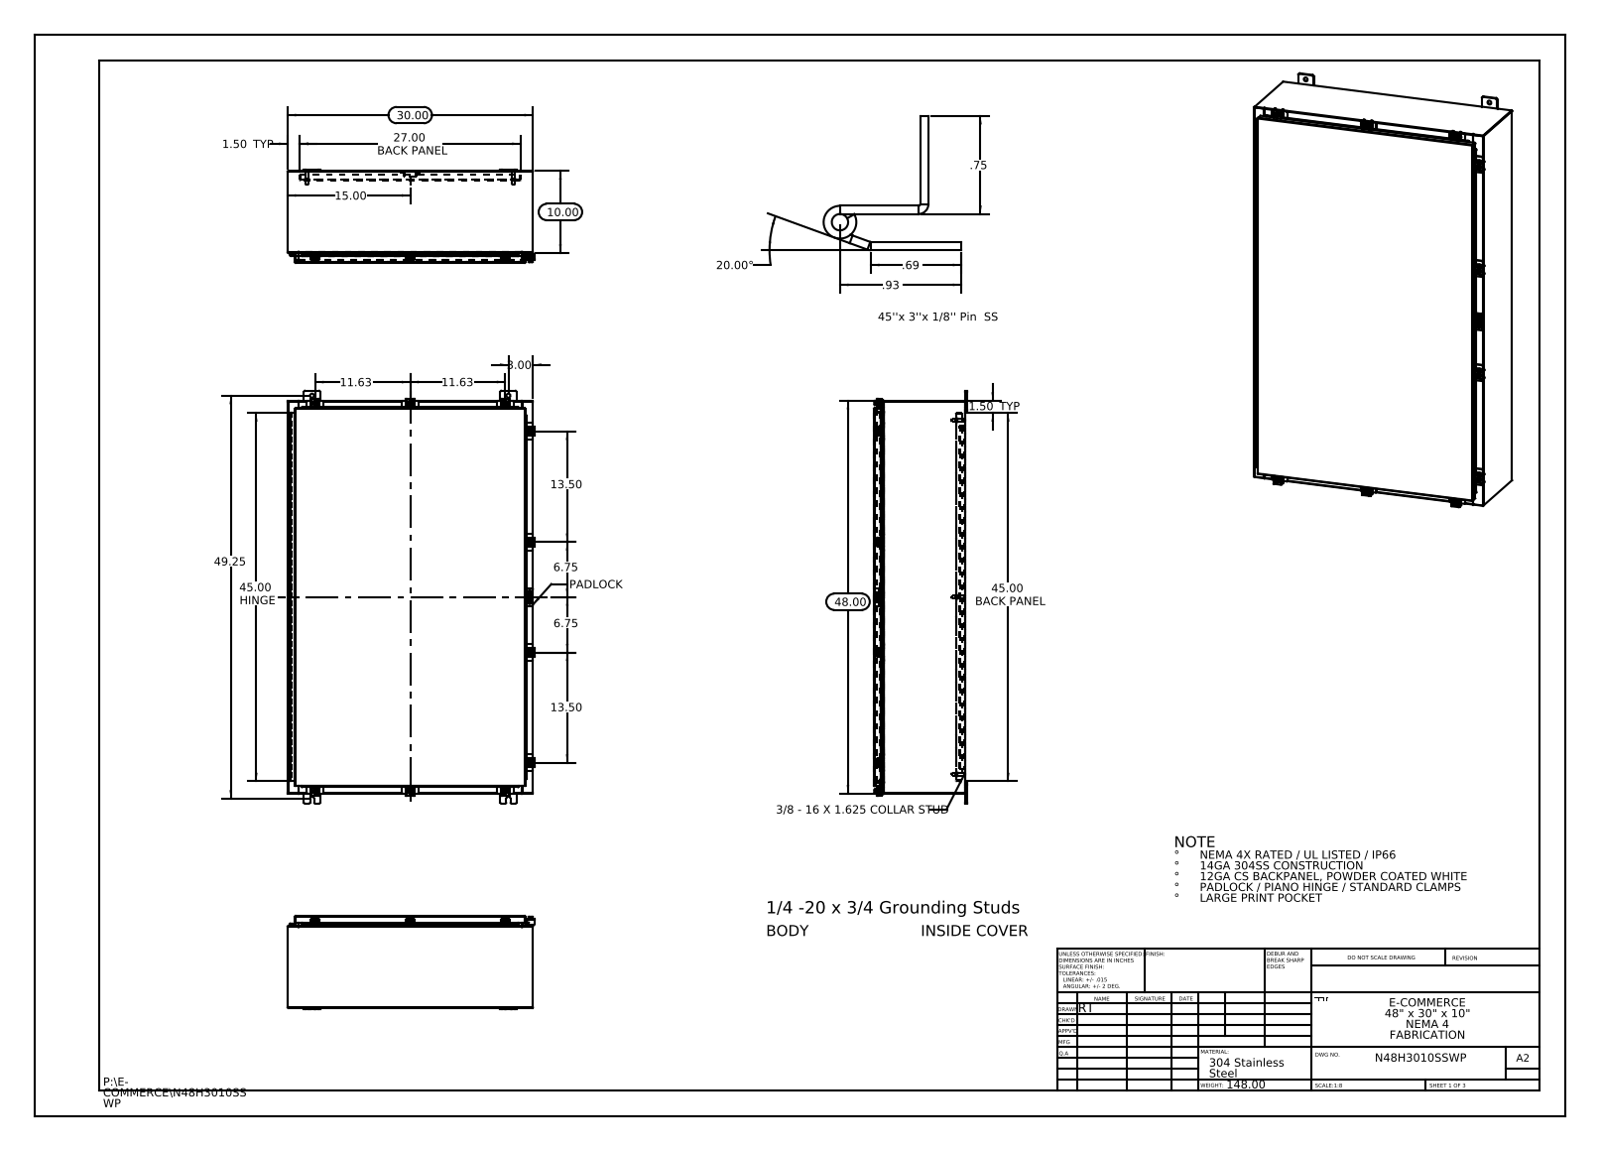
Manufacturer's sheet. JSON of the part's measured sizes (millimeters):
{"part_name": "N48H3010SSWP Cover; N48H3010SSWP Enclosure Stiffener; N48H3010SSWP Padlock Staple; N48H3010SSWP Top (+8 more)", "step_written_by": "SolidWorks 2013 (CONFIG_CONTROL_DESIGN)", "units": "millimeters", "bodies": {"solids": 70, "faces": 2861, "planar": 1492, "cylindrical": 1221, "other": 148}, "overall_size": [1282.7, 767.4, 289.3], "volume_mm3": 8498000, "surface_area_mm2": 8337000, "round_holes": [[5.4, 10], [6.6, 10], [12.7, 10], [3.2, 2], [3.2, 1]], "round_bosses_or_shafts": [[6.4, 11], [12.7, 10], [10.1, 10], [15.9, 6], [9.5, 6], [8.4, 6]], "partial_cylinders_radius": [[1.5, 46], [0.3, 31], [2.2, 25], [4.8, 24], [3, 20], [3.6, 20], [1.3, 15], [2, 14]], "face_to_face_distances": [1.9, 282.6, 280.7, 2.6, 284.5, 25.4, 257.2, 27.3, 255.3, 29.9], "hole_center_spacings": [549.3, 682.7, 844.4, 1152.2, 1195.7, 1240.9, 342.9, 641.4]}
